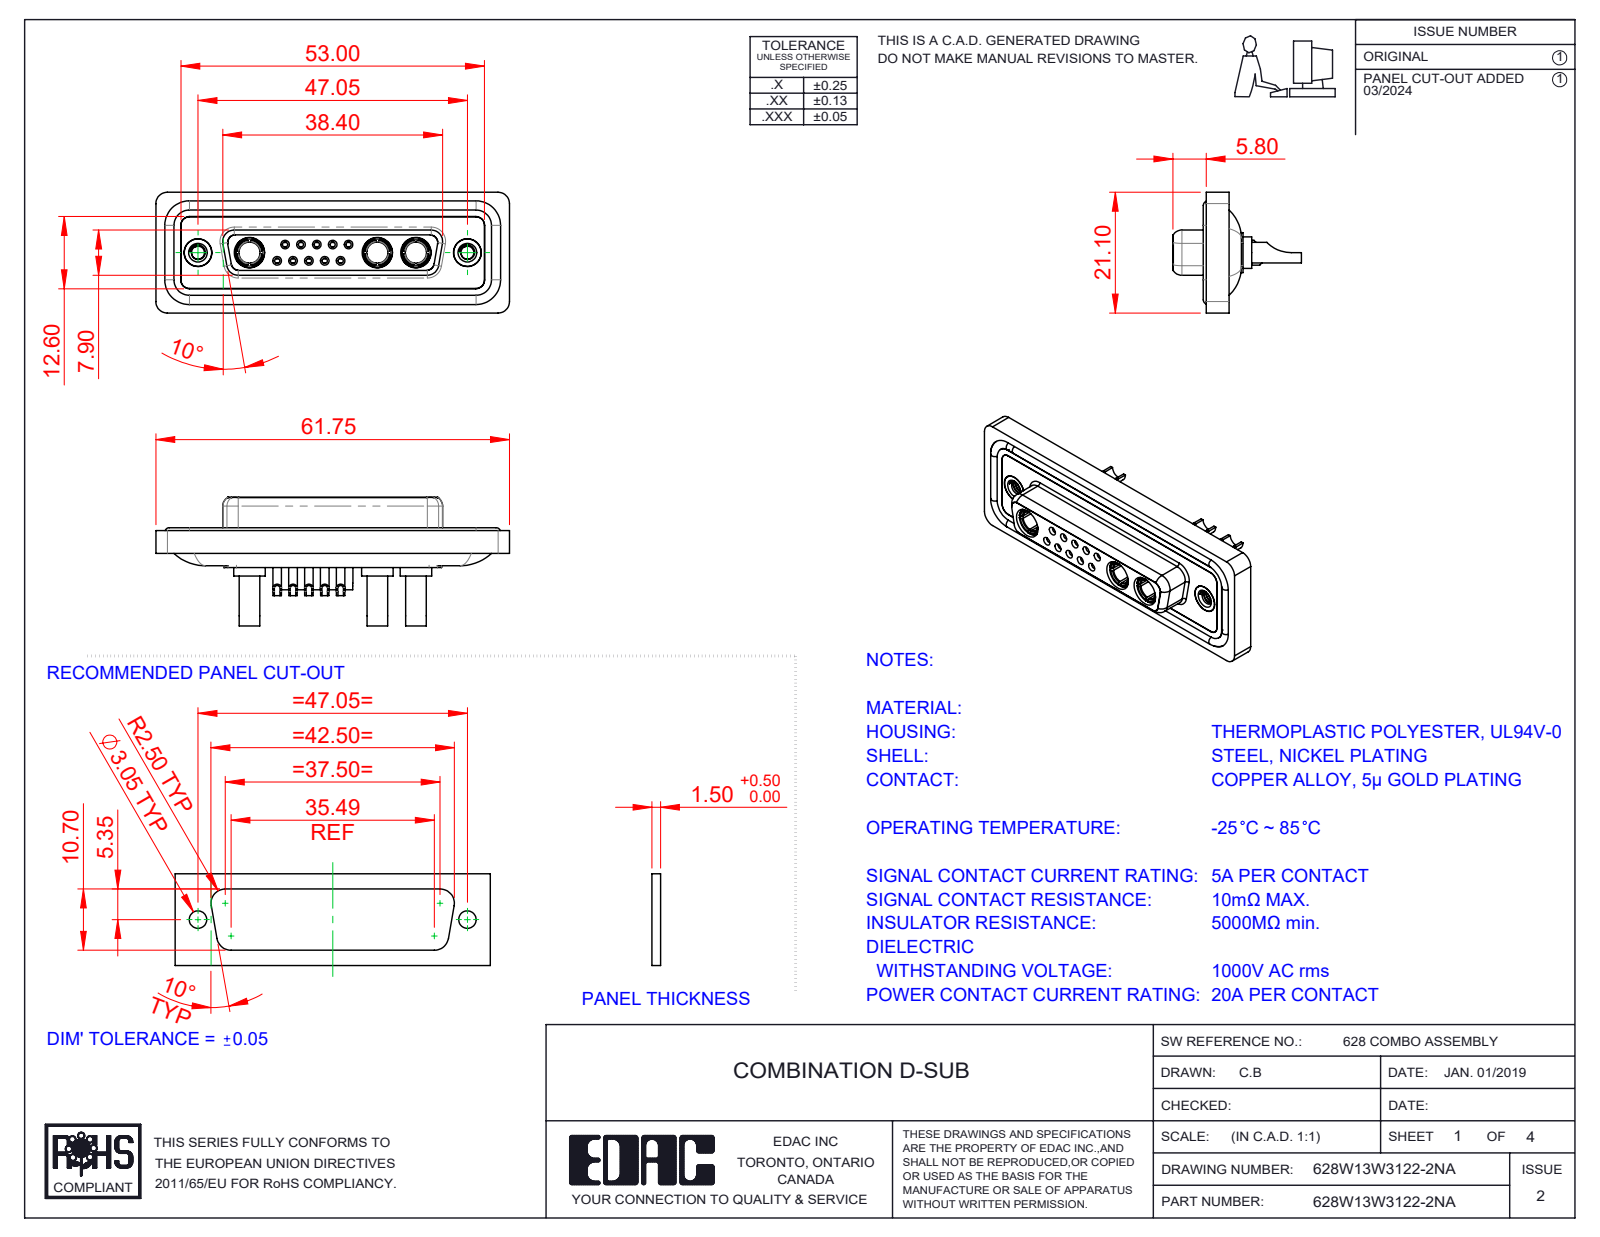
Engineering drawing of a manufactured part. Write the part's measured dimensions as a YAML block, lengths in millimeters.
part_name: "628Combo Waterproof Housing_25 Contacts; 628Combo Contact Row 2_22; 628Combo Shell Front_25 Contacts; 628Combo Shell Rear_25 Contacts (+5 more)"
step_written_by: "SolidWorks 2023 (CONFIG_CONTROL_DESIGN)"
units: millimeters
bodies: {solids: 23, faces: 1174, planar: 371, cylindrical: 478, other: 325}
overall_size: [61.75, 22.45, 21.1]
volume: 8334
surface_area: 14059
round_holes:
  - {diameter: 0.9, count: 10}
  - {diameter: 1, count: 10}
  - {diameter: 1.1, count: 10}
  - {diameter: 1.5, count: 10}
  - {diameter: 2, count: 10}
  - {diameter: 1.6, count: 5}
  - {diameter: 1.7, count: 5}
  - {diameter: 4.85, count: 5}
  - {diameter: 2.7, count: 3}
  - {diameter: 3.7, count: 3}
  - {diameter: 5.3, count: 3}
  - {diameter: 2.26, count: 2}
round_bosses_or_shafts:
  - {diameter: 2.2, count: 10}
  - {diameter: 1.6, count: 9}
  - {diameter: 5.5, count: 3}
  - {diameter: 5.2, count: 3}
  - {diameter: 4.96, count: 3}
  - {diameter: 4.75, count: 3}
  - {diameter: 3.75, count: 3}
  - {diameter: 3.6, count: 3}
partial_cylinders:
  - {radius: 1.5, count: 22}
  - {radius: 2, count: 18}
  - {radius: 1.35, count: 8}
  - {radius: 1.6, count: 8}
  - {radius: 1, count: 6}
  - {radius: 0.25, count: 4}
  - {radius: 0.5, count: 4}
  - {radius: 0.6, count: 4}
face_to_face_distances: [0.4, 1.8, 7.45, 5.65, 0.5, 6.6, 7.05, 1.6, 2.9, 1.1]
hole_center_spacings: [3.16, 2.77, 5.03, 5.04, 5.54, 8.31, 7.49, 2.76]
